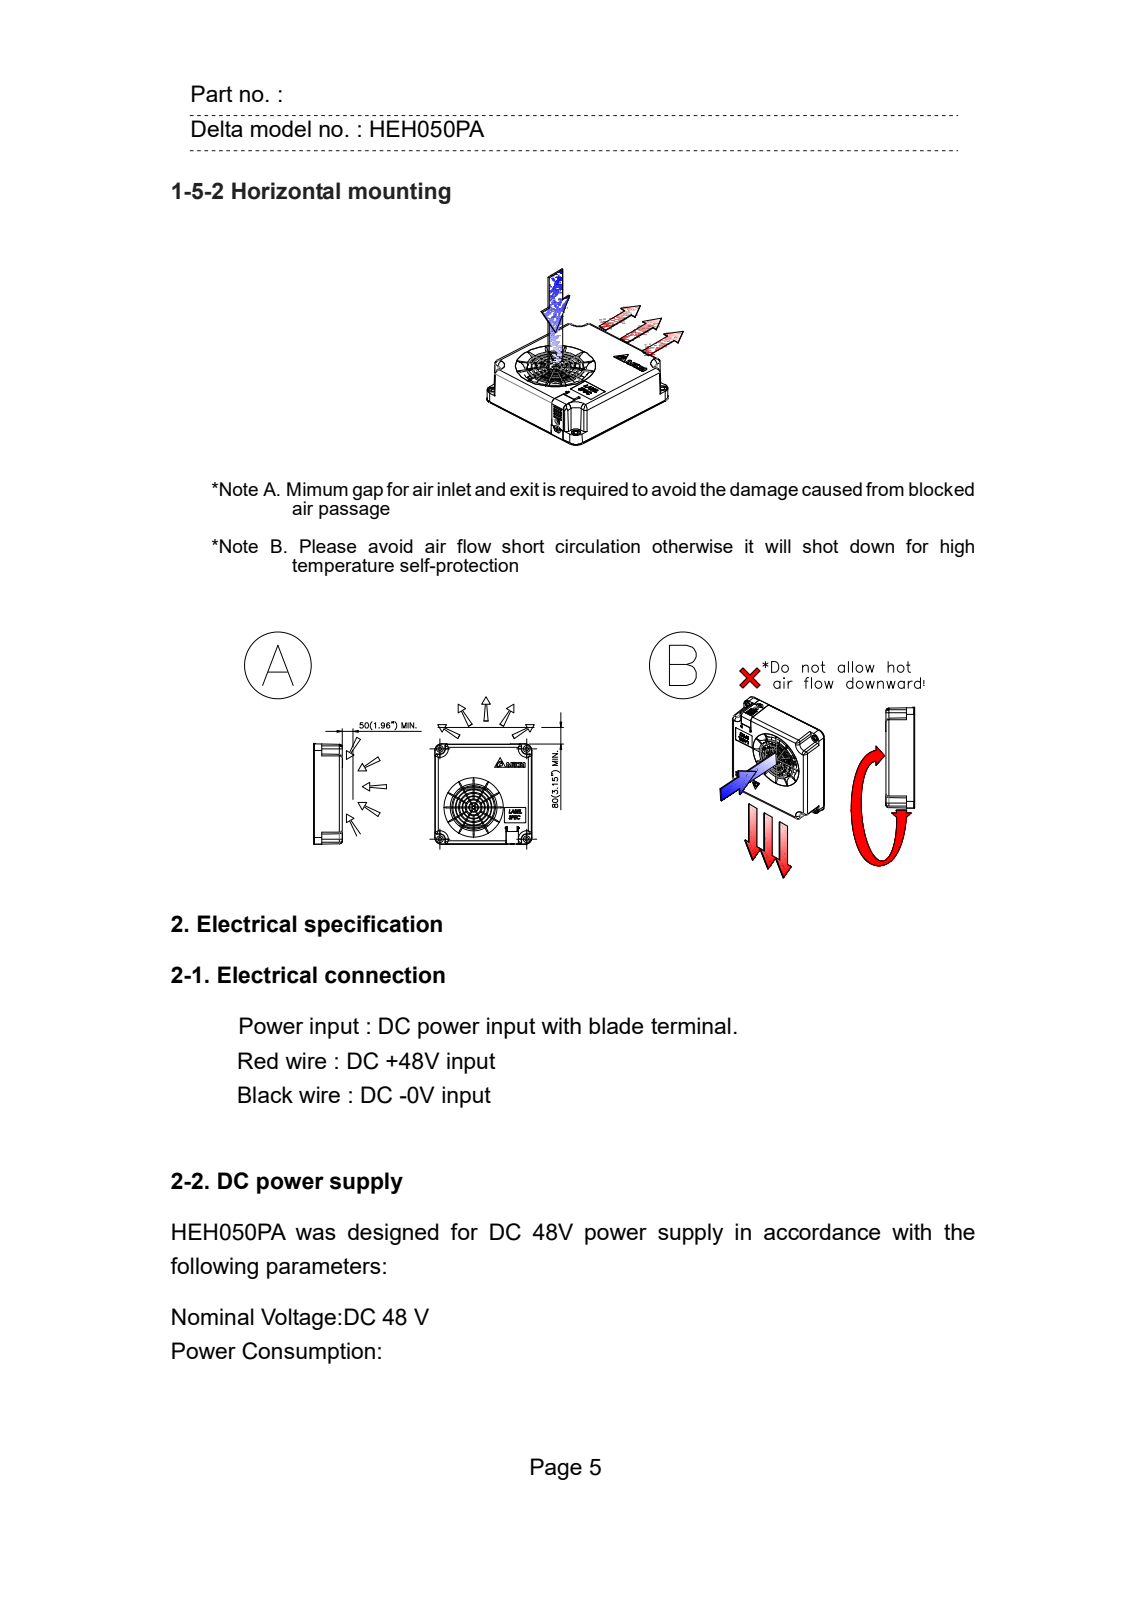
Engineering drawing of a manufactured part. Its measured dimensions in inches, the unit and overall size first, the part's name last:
Units: inches
Overall size (bounding box): 5.932 × 5.734 × 1.705
Round holes (diameter × count): ⌀0.209 ×4, ⌀0.209 ×4, ⌀0.352 ×4, ⌀0.394 ×4, ⌀0.128 ×3, ⌀0.079 ×1, ⌀0.098 ×1, ⌀0.134 ×1, ⌀0.161 ×1, ⌀0.197 ×1, ⌀0.236 ×1, ⌀0.315 ×1
Round bosses / shafts (diameter × count): ⌀2.559 ×1, ⌀2.138 ×1, ⌀1.772 ×1, ⌀1.35 ×1, ⌀0.563 ×1, ⌀0.276 ×1, ⌀0.158 ×1, ⌀0.063 ×1
Partial cylindrical surfaces — rounded edges, fillets, slot ends (radius × count): R0.02 ×17, R0.039 ×17, R0.138 ×16, R0.03 ×14, R0.02 ×12, R0.079 ×11, R0.177 ×8, R0.049 ×5
Main face-to-face distances: 0.047, 0.119, 0.071, 1.425, 1.543, 1.496, 0.079, 1.575, 1.622, 1.504
Hole centre spacings: 5.118, 5.141, 5.315, 5.339, 0.504, 4.846, 5.263, 7.136
Volume: 46.26 in³ · Surface area: 294.3 in²
Bodies: 1 solid, 2045 faces (1009 planar, 585 cylindrical, 451 other)
Part name (STEP PRODUCT): HEH050ba
STEP written by: SolidWorks 2013 (AUTOMOTIVE_DESIGN)
